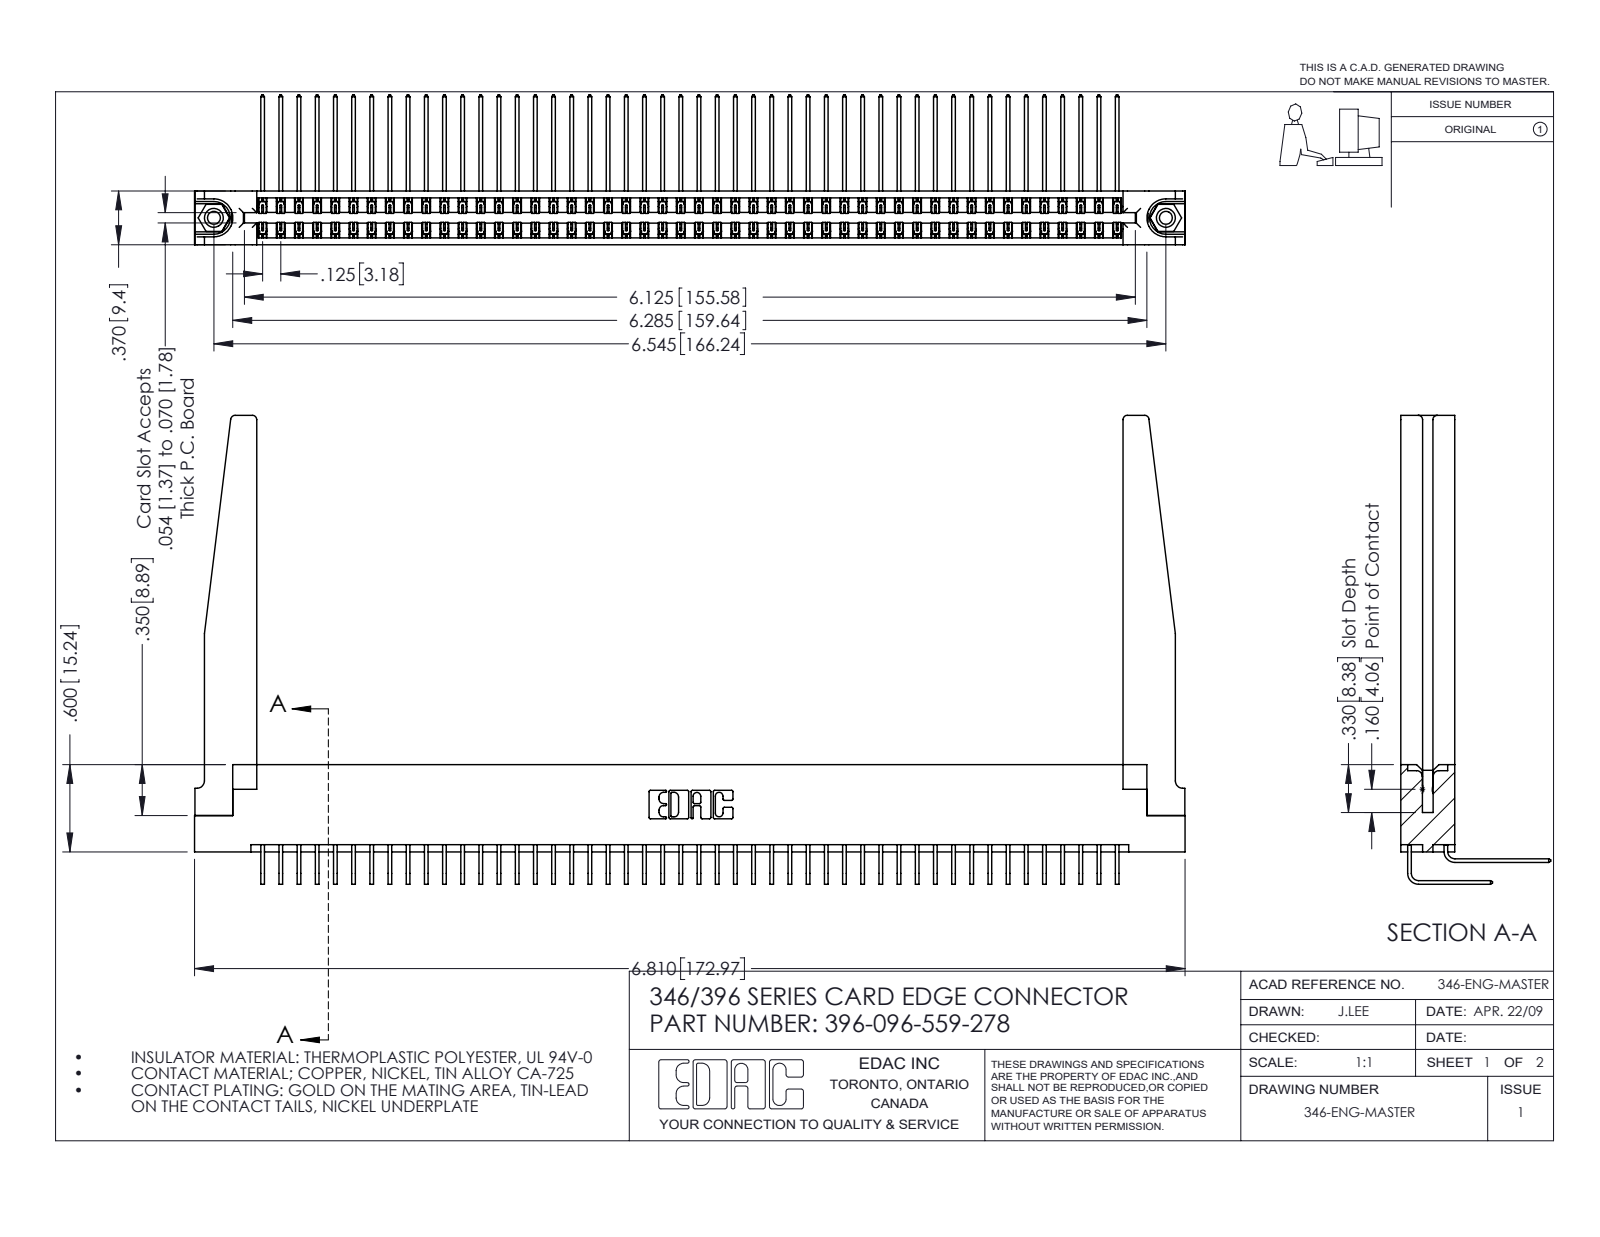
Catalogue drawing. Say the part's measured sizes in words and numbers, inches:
The part is named "345-250-001_345-250-001-102; 345-292-001_559 Tail - 2; 346 Part_Flush Mounting Lugs - 0.156 Dia-TH; 345-292-001_558 559 Tail - 1 (+2 more)". Its 3-D file was written by "SolidWorks 2016 (CONFIG_CONTROL_DESIGN)". It is 101 solids with 5540 faces: 3770 planar, 1718 cylindrical and 52 other. Overall it measures 6.81 by 3.223 by 1.03 inches. Its volume is 1.488 cubic inches and its surface area 51.61 square inches. Round holes: 2 of diameter 0.089, 2 of diameter 0.125, 2 of diameter 0.156, 1 of diameter 0.064. Round bosses or shafts: 2 of diameter 0.155. Partial cylindrical surfaces (rounded edges, fillets, slot ends): 144 of radius 0.006, 22 of radius 0.01, 8 of radius 0.03, 6 of radius 0.007, 6 of radius 0.031, 4 of radius 0.05, 3 of radius 0.026, 2 of radius 0.014. The main face-to-face distances are 0.048, 0.322, 0.37, 0.072, 0.025, 0.25, 0.298, 0.148, 0.15, 0.275. The hole center spacings are 0.246, 6.336, 6.545.
